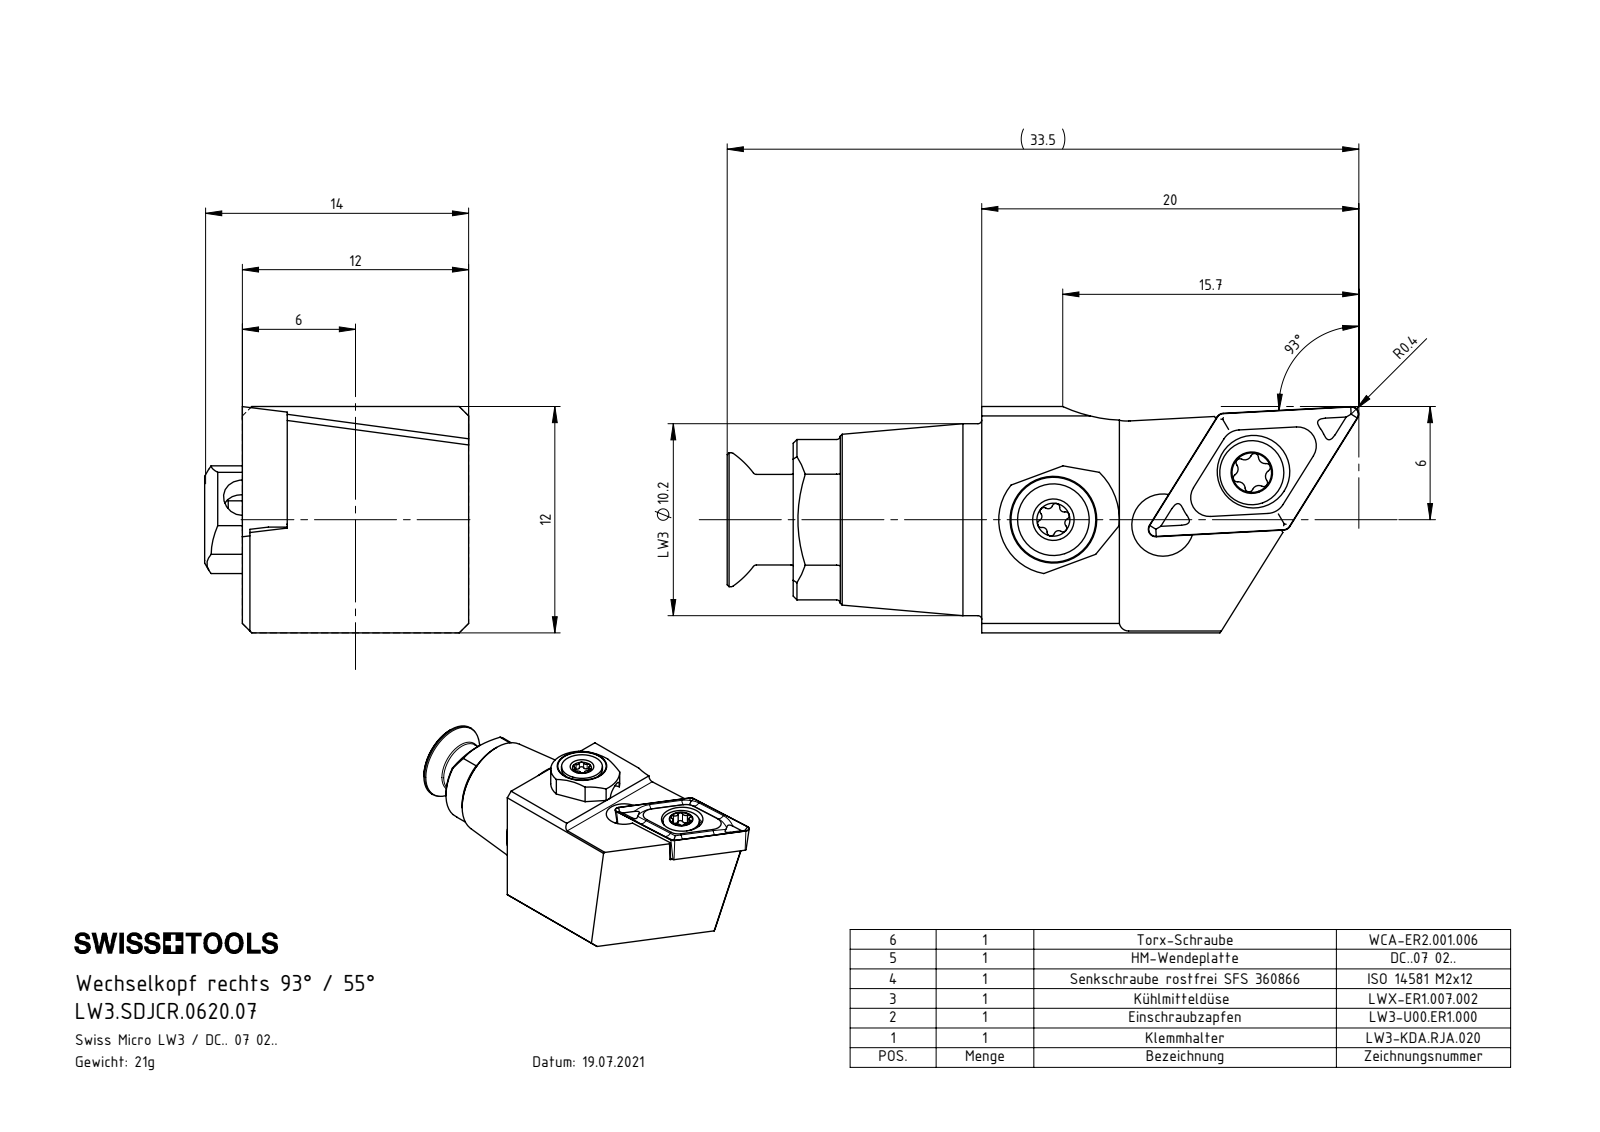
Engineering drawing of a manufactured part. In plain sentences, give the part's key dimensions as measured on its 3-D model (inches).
The part is named "LW3-U00.ER1.000_B; LW3.SDJCR.0620.07; ISO 14581 - M2x12; LW3-KDA.RJA.020_A (+3 more)". Its 3-D file was written by "SolidWorks 2022 (CONFIG_CONTROL_DESIGN)". It is 6 solids with 253 faces: 70 planar, 79 cylindrical and 104 other. Overall it measures 1.315 by 0.551 by 0.472 inches. Its volume is 0.164 cubic inches and its surface area 3.574 square inches. Round holes: 1 of diameter 0.063, 1 of diameter 0.079, 1 of diameter 0.081, 1 of diameter 0.098, 1 of diameter 0.11, 1 of diameter 0.118, 1 of diameter 0.13, 1 of diameter 0.152, 1 of diameter 0.217. Round bosses or shafts: 1 of diameter 0.401, 1 of diameter 0.272, 1 of diameter 0.236, 1 of diameter 0.197, 1 of diameter 0.189, 1 of diameter 0.15, 1 of diameter 0.134, 1 of diameter 0.098. Partial cylindrical surfaces (rounded edges, fillets, slot ends): 8 of radius 0.008, 6 of radius 0.008, 6 of radius 0.009, 4 of radius 0.014, 2 of radius 0.014, 1 of radius 0.02, 1 of radius 0.039, 1 of radius 0.114. The main face-to-face distances are 0.472, 0.379, 0.094, 0.457, 0.078, 0.016, 0.079, 0.098, 0.528, 0.449. The hole center spacings are 0.215, 0.219, 0.23, 0.426, 0.43.
